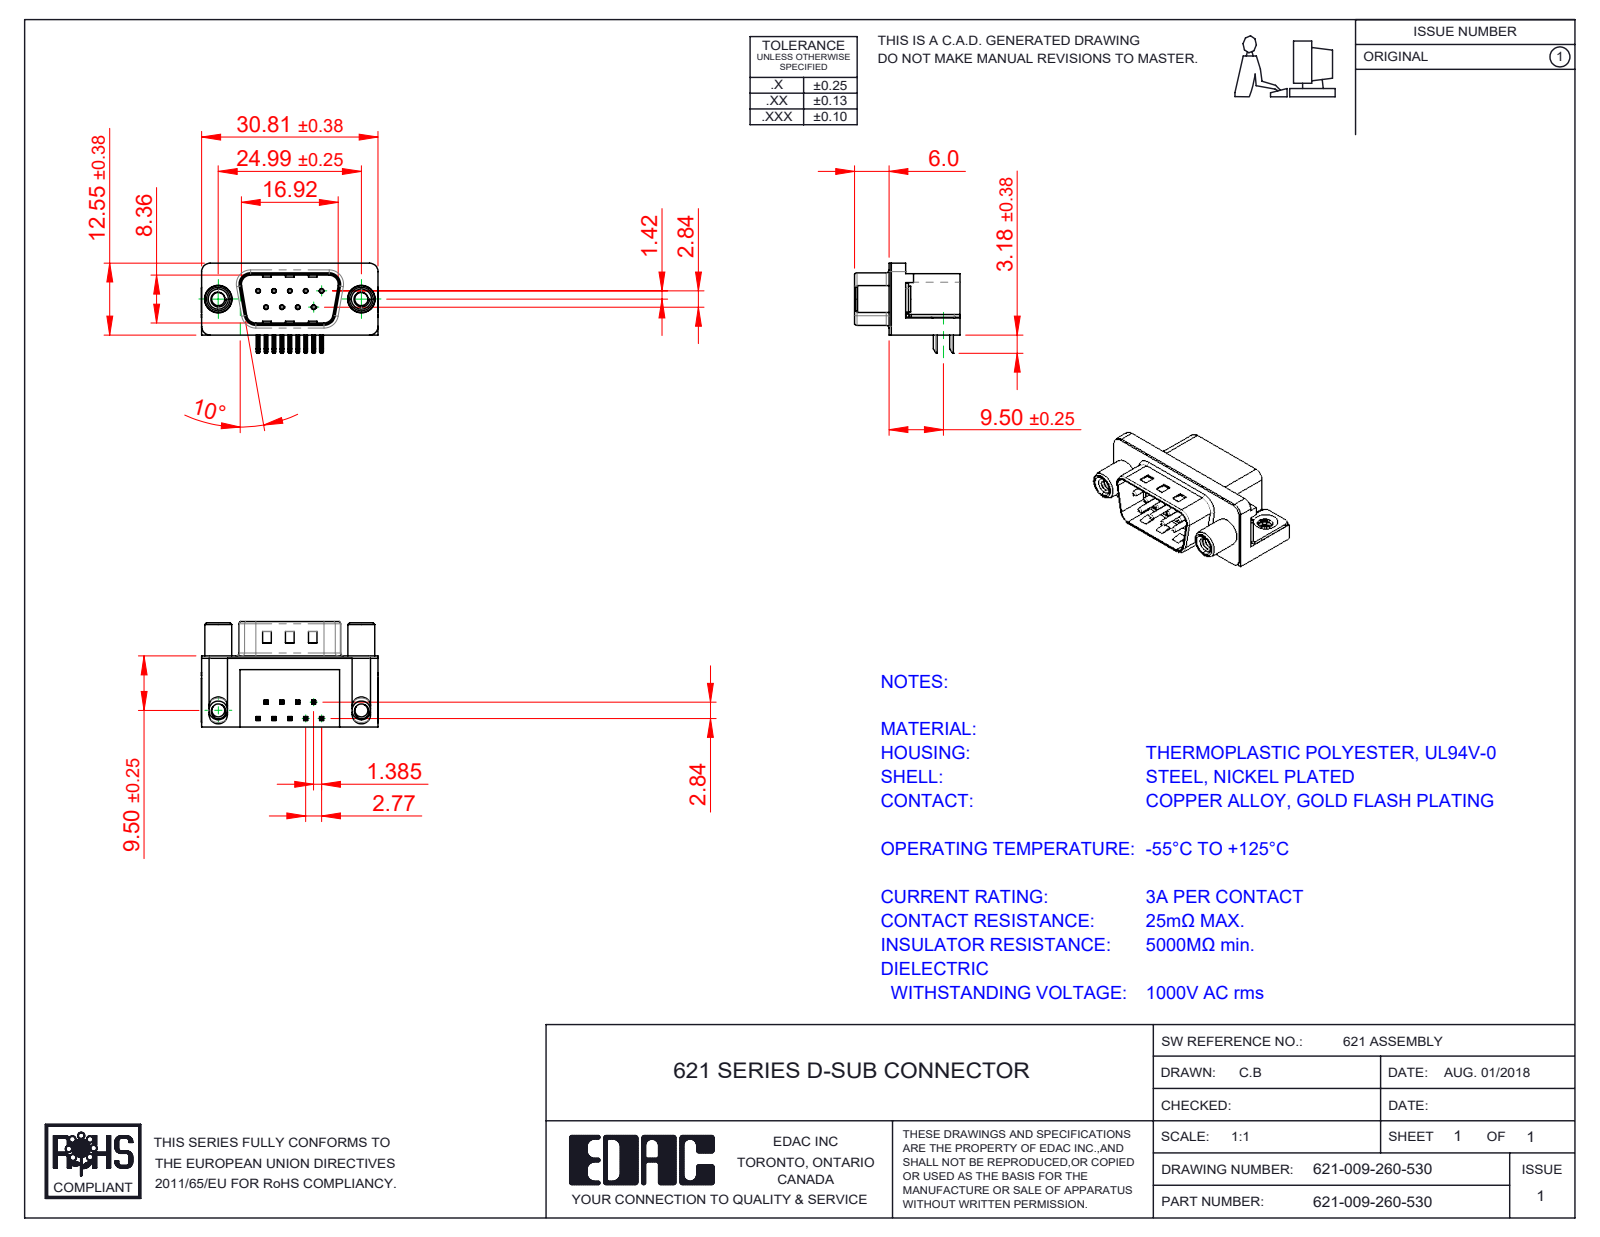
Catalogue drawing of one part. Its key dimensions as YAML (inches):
part_name: "621 Contact Top; 621-009-260-530; 621 2 Prong Board Lock; 621 Shell_9 Socket (+3 more)"
step_written_by: "SolidWorks 2016 (CONFIG_CONTROL_DESIGN)"
units: inches
bodies: {solids: 15, faces: 1025, planar: 597, cylindrical: 331, other: 97}
overall_size: [1.216, 0.724, 0.64]
volume: 0.204
surface_area: 7.17
round_holes:
  - {diameter: 0.014, count: 9}
  - {diameter: 0.031, count: 9}
  - {diameter: 0.091, count: 2}
  - {diameter: 0.122, count: 2}
  - {diameter: 0.157, count: 2}
  - {diameter: 0.189, count: 2}
  - {diameter: 0.197, count: 2}
round_bosses_or_shafts:
  - {diameter: 0.03, count: 9}
  - {diameter: 0.193, count: 2}
  - {diameter: 0.185, count: 2}
  - {diameter: 0.177, count: 2}
  - {diameter: 0.152, count: 2}
partial_cylinders:
  - {radius: 0.01, count: 36}
  - {radius: 0.005, count: 18}
  - {radius: 0.039, count: 16}
  - {radius: 0.02, count: 14}
  - {radius: 0.059, count: 8}
  - {radius: 0.063, count: 8}
  - {radius: 0.013, count: 4}
  - {radius: 0.035, count: 4}
face_to_face_distances: [0.016, 0.472, 0.488, 0.407, 0.374, 0.098, 0.114, 0.02, 0.083, 0.014]
hole_center_spacings: [0.124, 0.109, 0.218, 0.198, 0.198, 0.327, 0.294, 0.295]
